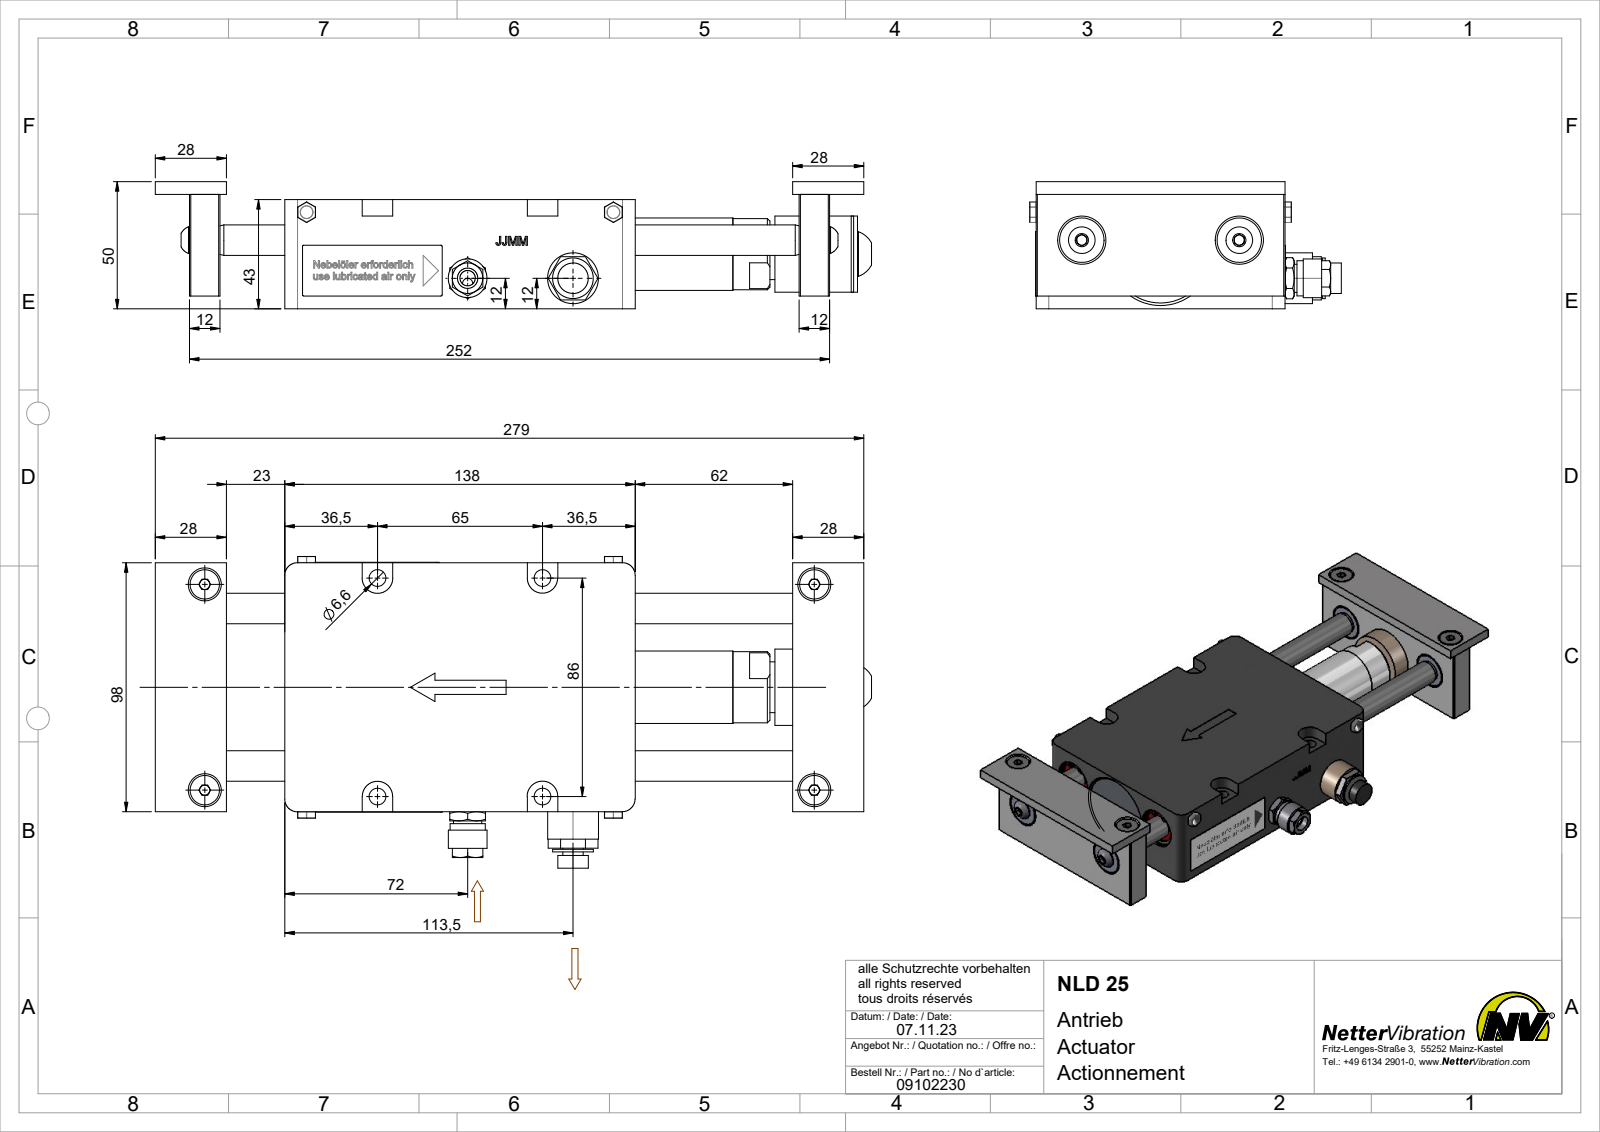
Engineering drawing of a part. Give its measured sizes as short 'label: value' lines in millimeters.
name: NLD 25 drive unit-09102230
written by: SolidWorks 2023 (AUTOMOTIVE_DESIGN)
unit: mm
bodies: 47 solids, 1256 faces (565 planar, 397 cylindrical, 294 other)
size: 282 × 122.7 × 50
volume: 730 497 mm³; area: 182 614 mm²
holes: 10× ⌀6.6, 8× ⌀5, 3× ⌀6, 3× ⌀8, 2× ⌀4, 2× ⌀4.2, 2× ⌀12.2, 2× ⌀12.5, 2× ⌀18, 1× ⌀6.5, 1× ⌀6.81, 1× ⌀8.5
bosses: 4× ⌀11.57, 4× ⌀6, 3× ⌀17.5, 3× ⌀12, 2× ⌀20, 2× ⌀10.5, 2× ⌀5, 1× ⌀40
rounds: 60× R0.1, 4× R0.5, 4× R1, 4× R5, 4× R6
face distances: 43, 12, 45, 240, 2, 98, 5, 7, 1, 50
hole spacings: 13.5, 18.34, 31.48, 44.84, 65, 81, 85.54, 86
